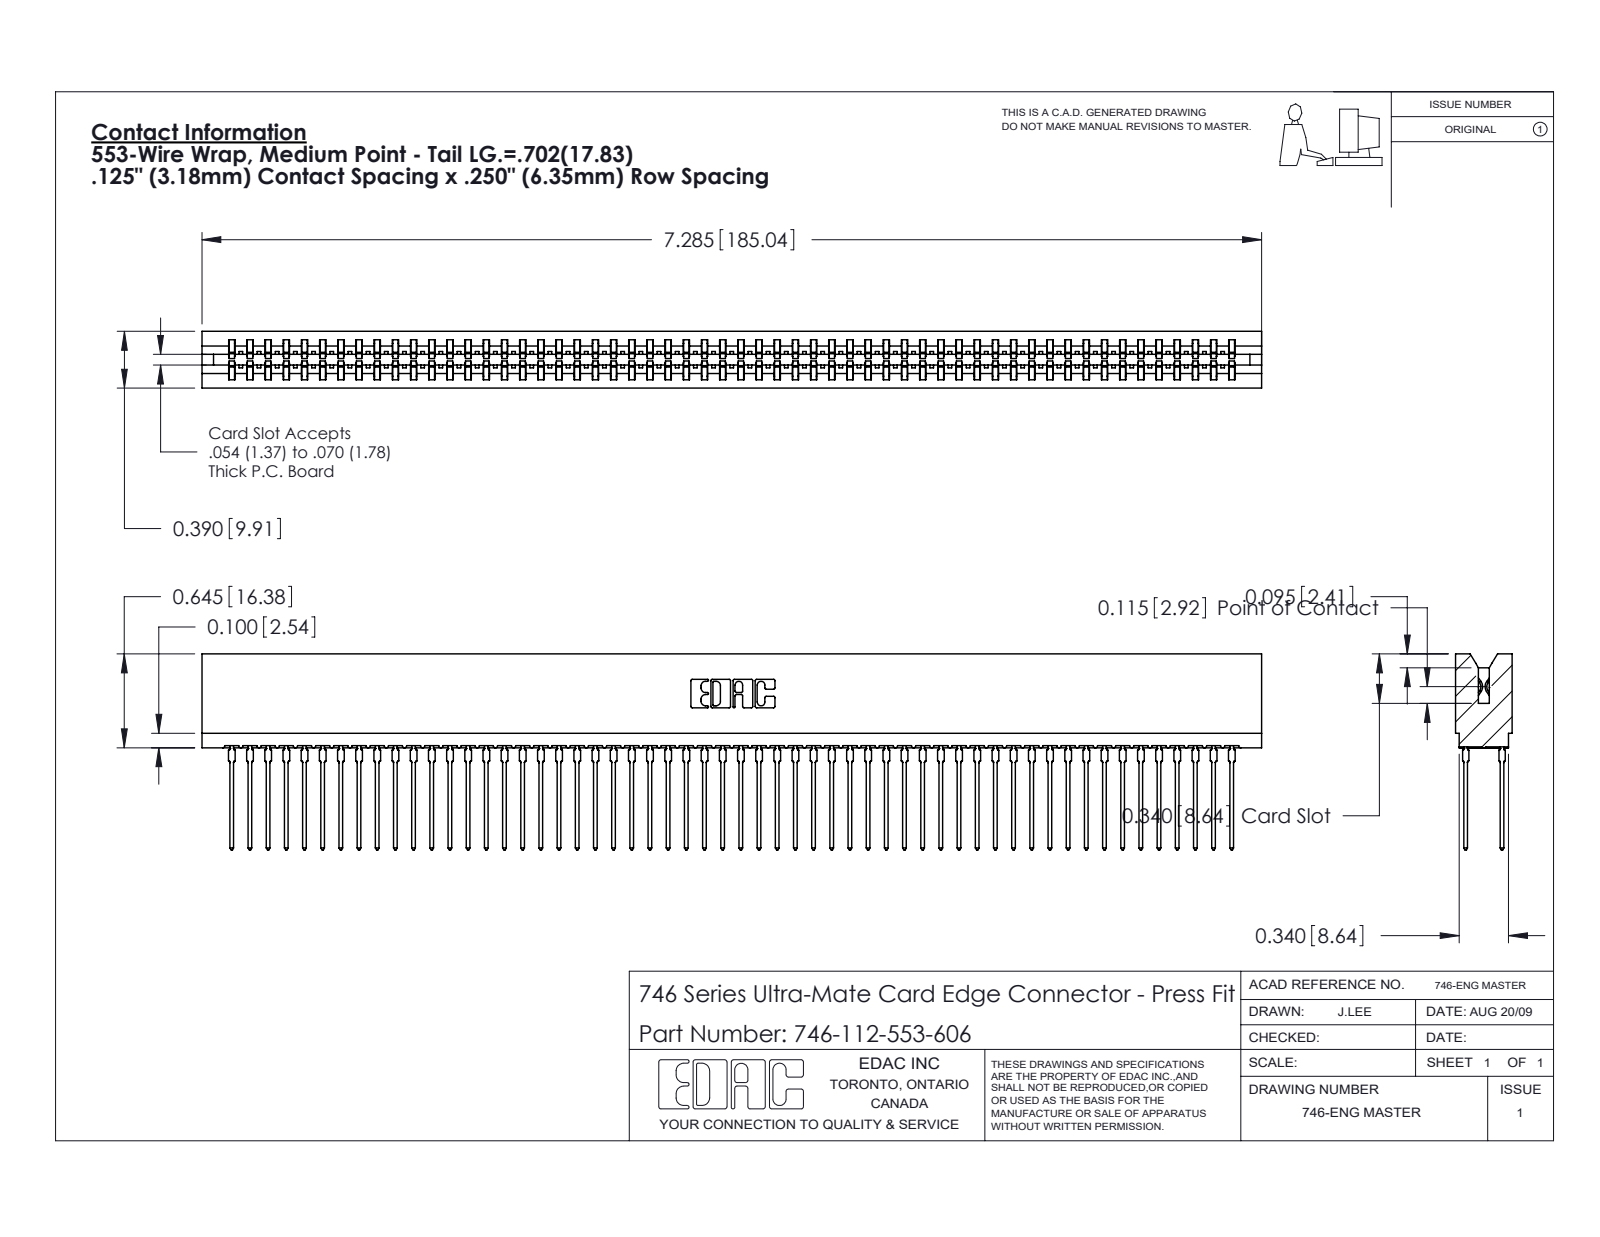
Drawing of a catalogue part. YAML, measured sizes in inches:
part_name: "746-292-001_553; 746 Part_.340 Slot Depth - 06; 746-112-553-606"
step_written_by: "SolidWorks 2020 (CONFIG_CONTROL_DESIGN)"
units: inches
bodies: {solids: 113, faces: 10122, planar: 5208, cylindrical: 2002, other: 2912}
overall_size: [7.285, 1.346, 0.39]
volume: 1.323
surface_area: 53.3
partial_cylinders:
  - {radius: 0.021, count: 224}
  - {radius: 0.015, count: 57}
  - {radius: 0.01, count: 22}
  - {radius: 0.005, count: 8}
  - {radius: 0.011, count: 8}
  - {radius: 0.007, count: 6}
  - {radius: 0.031, count: 6}
  - {radius: 0.026, count: 3}
face_to_face_distances: [0.057, 0.333, 0.025, 0.25, 0.307, 0.39, 0.275, 0.083, 0.225, 0.015]
